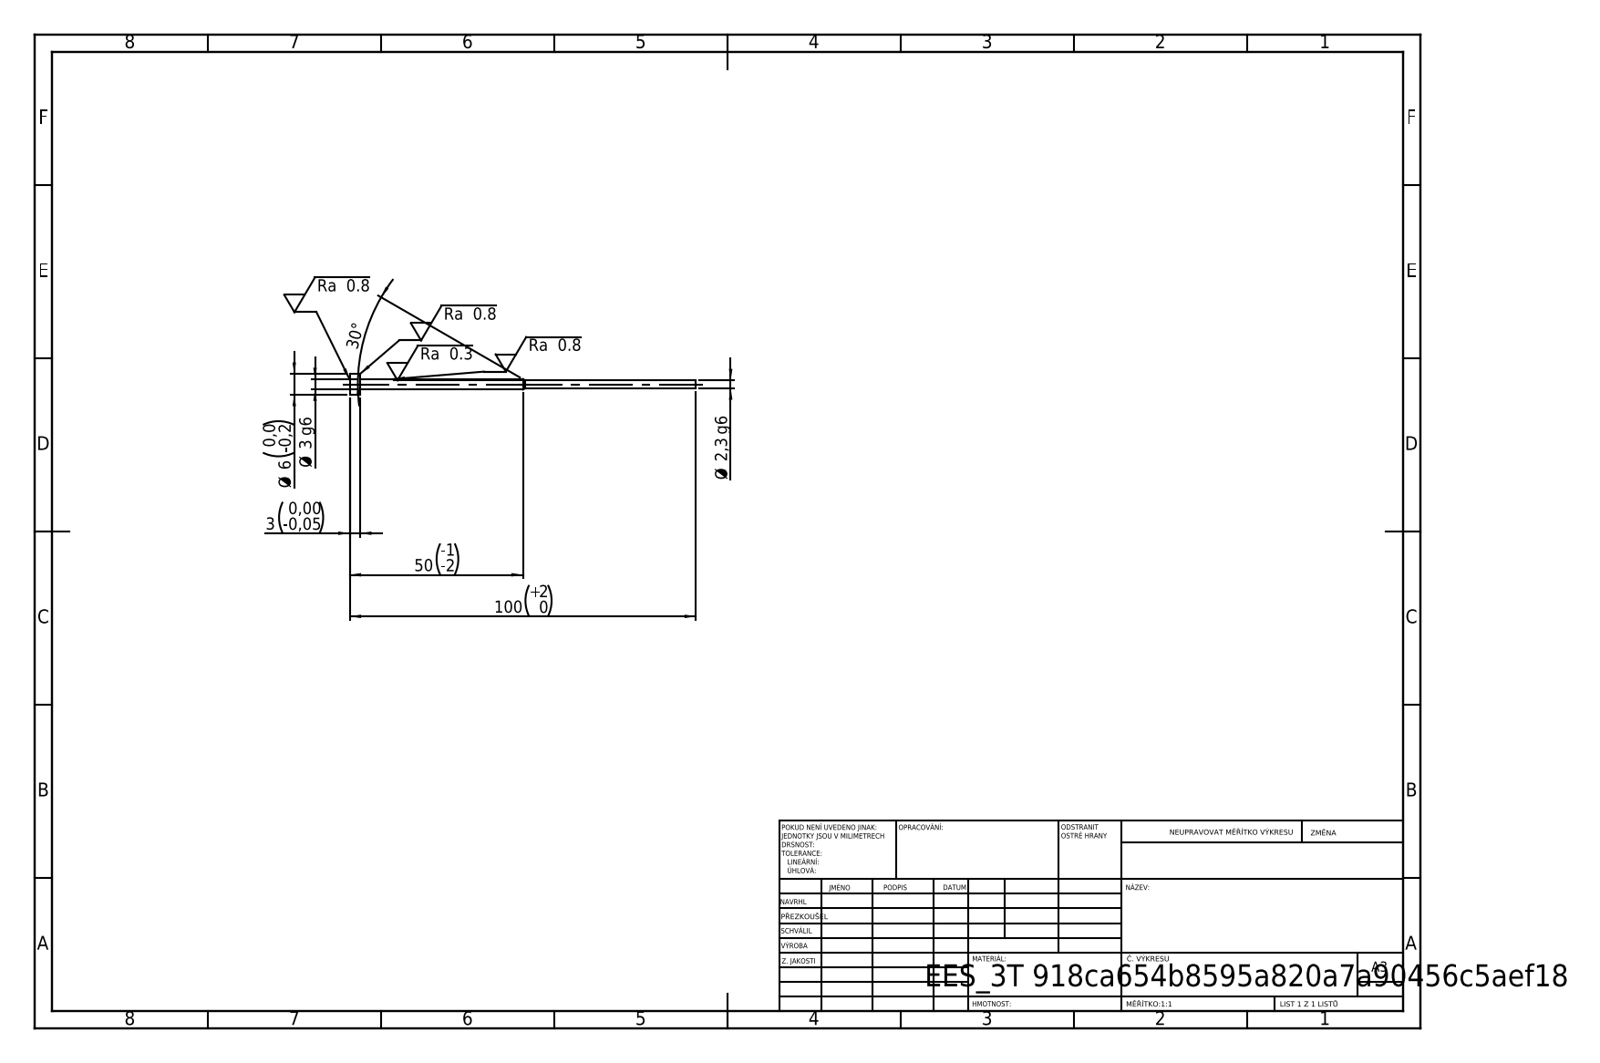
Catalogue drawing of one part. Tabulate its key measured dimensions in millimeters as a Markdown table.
| quantity | value |
| --- | --- |
| STEP written by | SolidWorks 2019 (CONFIG_CONTROL_DESIGN) |
| units | millimeters |
| bodies | 1 solid, 11 faces (3 planar, 6 cylindrical, 2 other) |
| overall size | 100 × 6 × 6 |
| volume | 626 mm³ |
| surface area | 916 mm² |
| round bosses / shafts (diameter × count) | 6 × 1, 3 × 1, 2.3 × 1 |
| main face-to-face distances | 3, 97, 100 |
